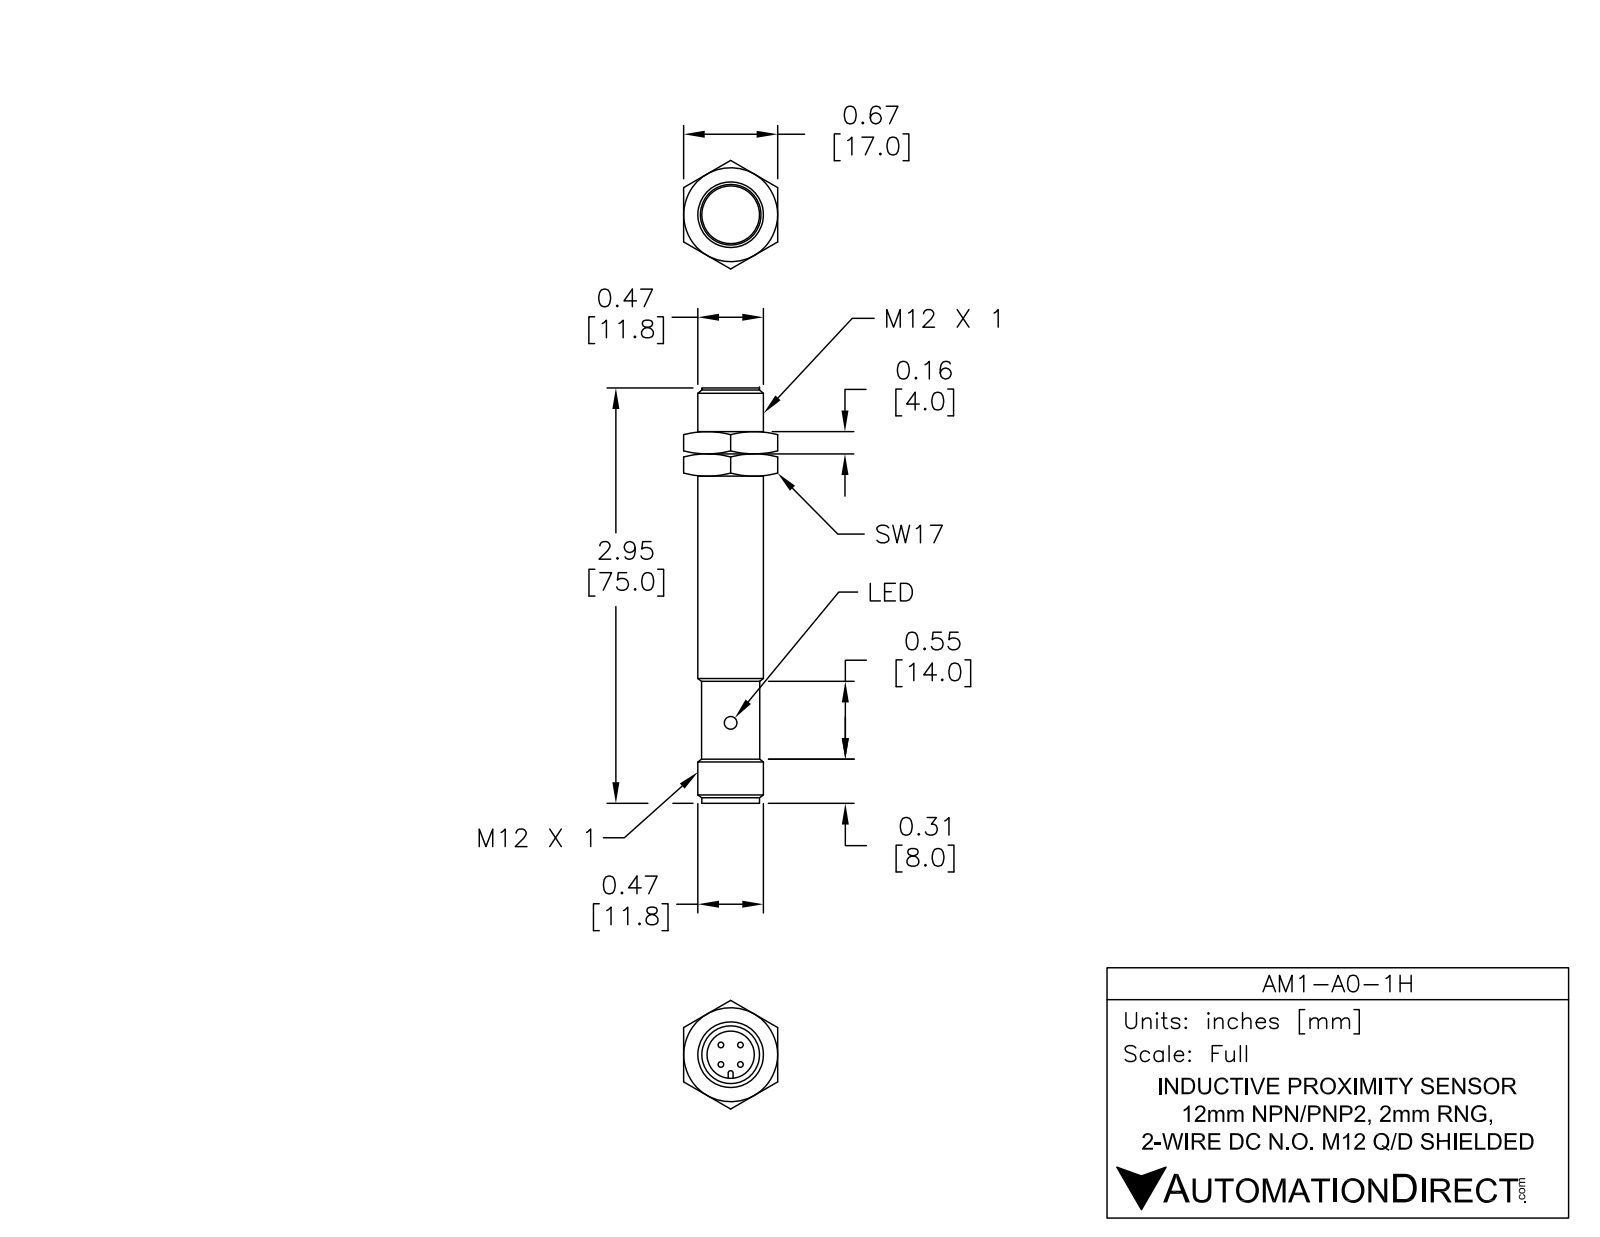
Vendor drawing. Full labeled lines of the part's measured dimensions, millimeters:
Part name (STEP PRODUCT): AM1-A0-1H
STEP written by: SolidWorks 2017 (AUTOMOTIVE_DESIGN)
Units: millimetres
Bodies: 3 solids, 112 faces (25 planar, 57 cylindrical, 30 other)
Overall size (bounding box): 74.8 × 12 × 12
Volume: 6 780 mm³ · Surface area: 4 583 mm²
Round holes (diameter × count): ⌀2.5 ×2, ⌀8.4 ×1, ⌀9.8 ×1
Round bosses / shafts (diameter × count): ⌀1 ×4, ⌀12 ×1, ⌀10.5 ×1, ⌀9.7 ×1, ⌀9.6 ×1
Partial cylindrical surfaces — rounded edges, fillets, slot ends (radius × count): R1.3 ×4, R0.5 ×1, R0.6 ×1, R1.3 ×1, R3.4 ×1
Main face-to-face distances: 0.5, 54.3, 53.8, 9.4, 63.7, 63.2, 8.9, 1, 65.9, 65.4
